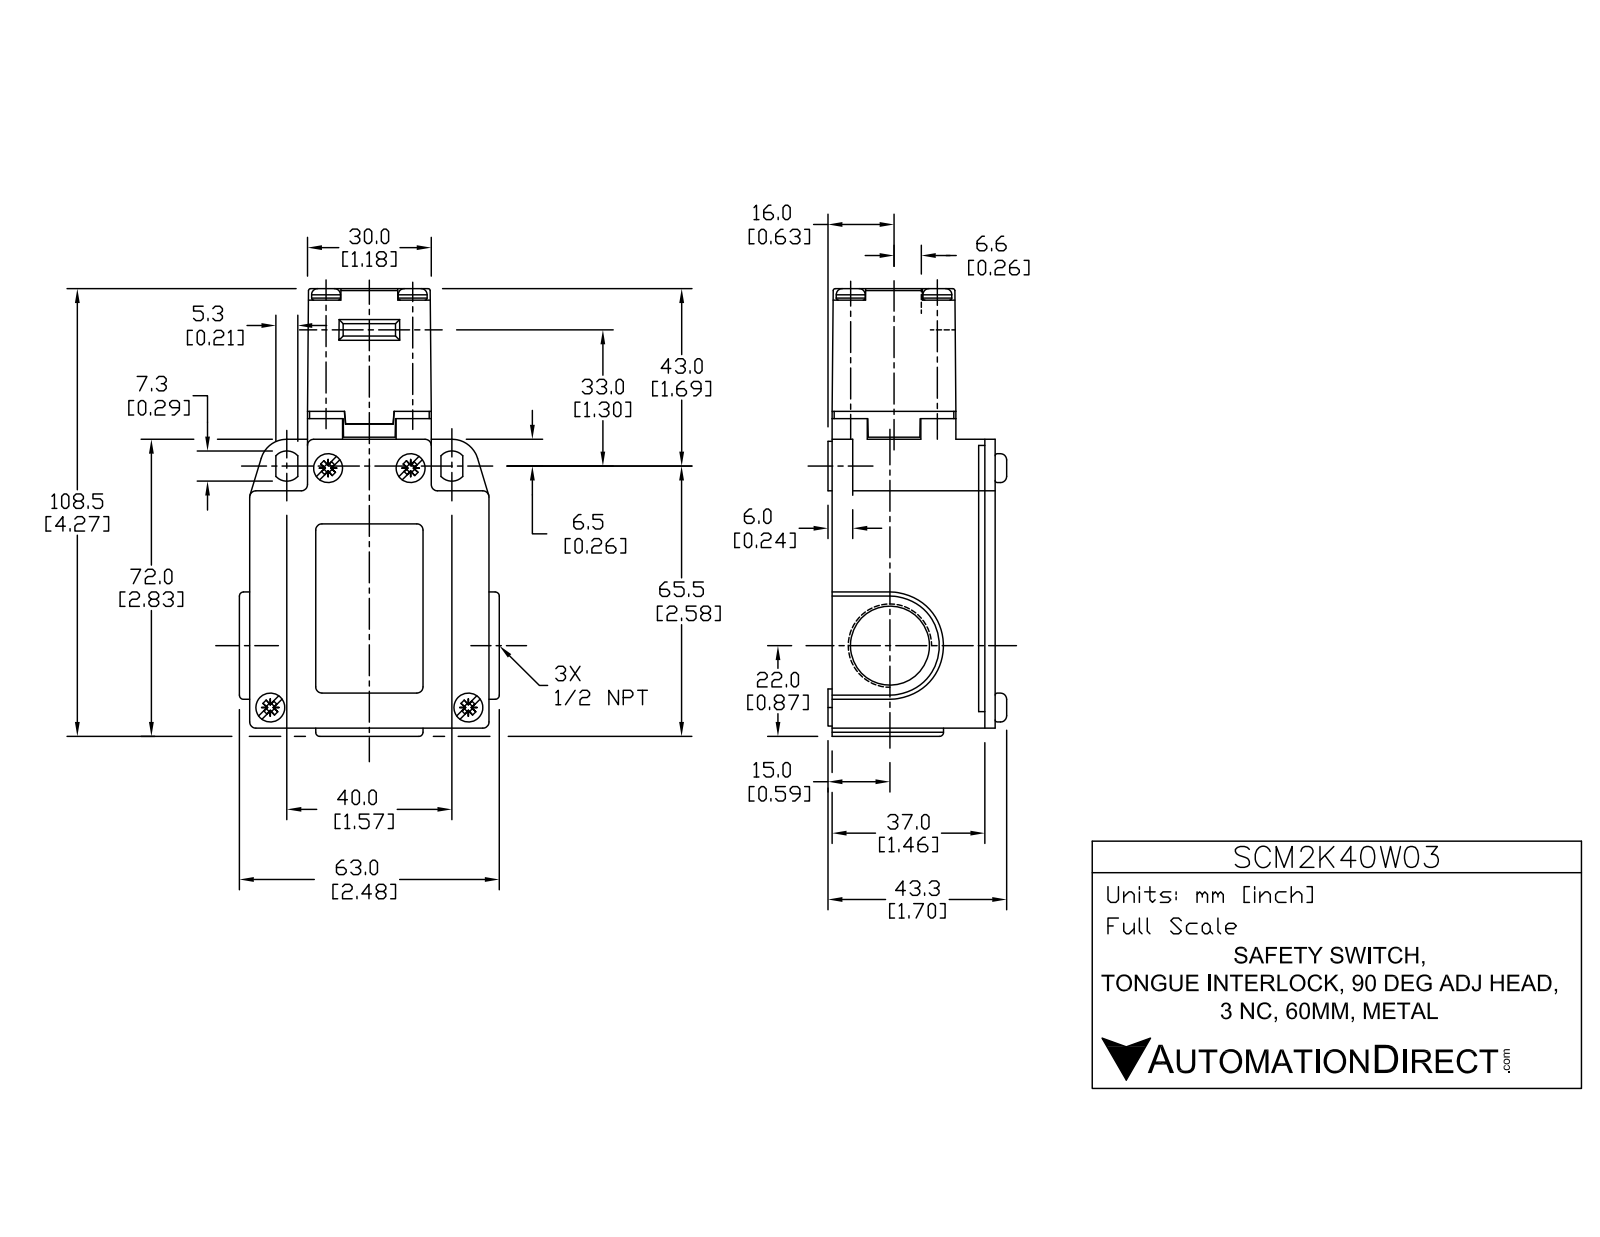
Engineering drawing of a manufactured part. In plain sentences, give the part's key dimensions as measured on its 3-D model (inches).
The part is named "SCM2K40W03". Its 3-D file was written by "SolidWorks 2017 (AUTOMOTIVE_DESIGN)". It is 2 solids with 206 faces: 106 planar, 78 cylindrical and 22 other. Overall it measures 4.272 by 2.441 by 1.705 inches. Its volume is 10.84 cubic inches and its surface area 43.53 square inches. Round holes: 2 of diameter 0.276, 2 of diameter 0.669, 2 of diameter 0.748. Round bosses or shafts: 6 of diameter 0.276, 2 of diameter 0.472, 2 of diameter 0.354. Partial cylindrical surfaces (rounded edges, fillets, slot ends): 12 of radius 0.059, 4 of radius 0.02, 2 of radius 0.144, 2 of radius 0.256, 2 of radius 0.512, 1 of radius 0.453, 1 of radius 0.472. The main face-to-face distances are 1.555, 1.732, 0.551, 1.181, 2.283, 0.079, 0.236, 0.374, 2.756, 0.118. The hole center spacings are 0.557, 0.827.
